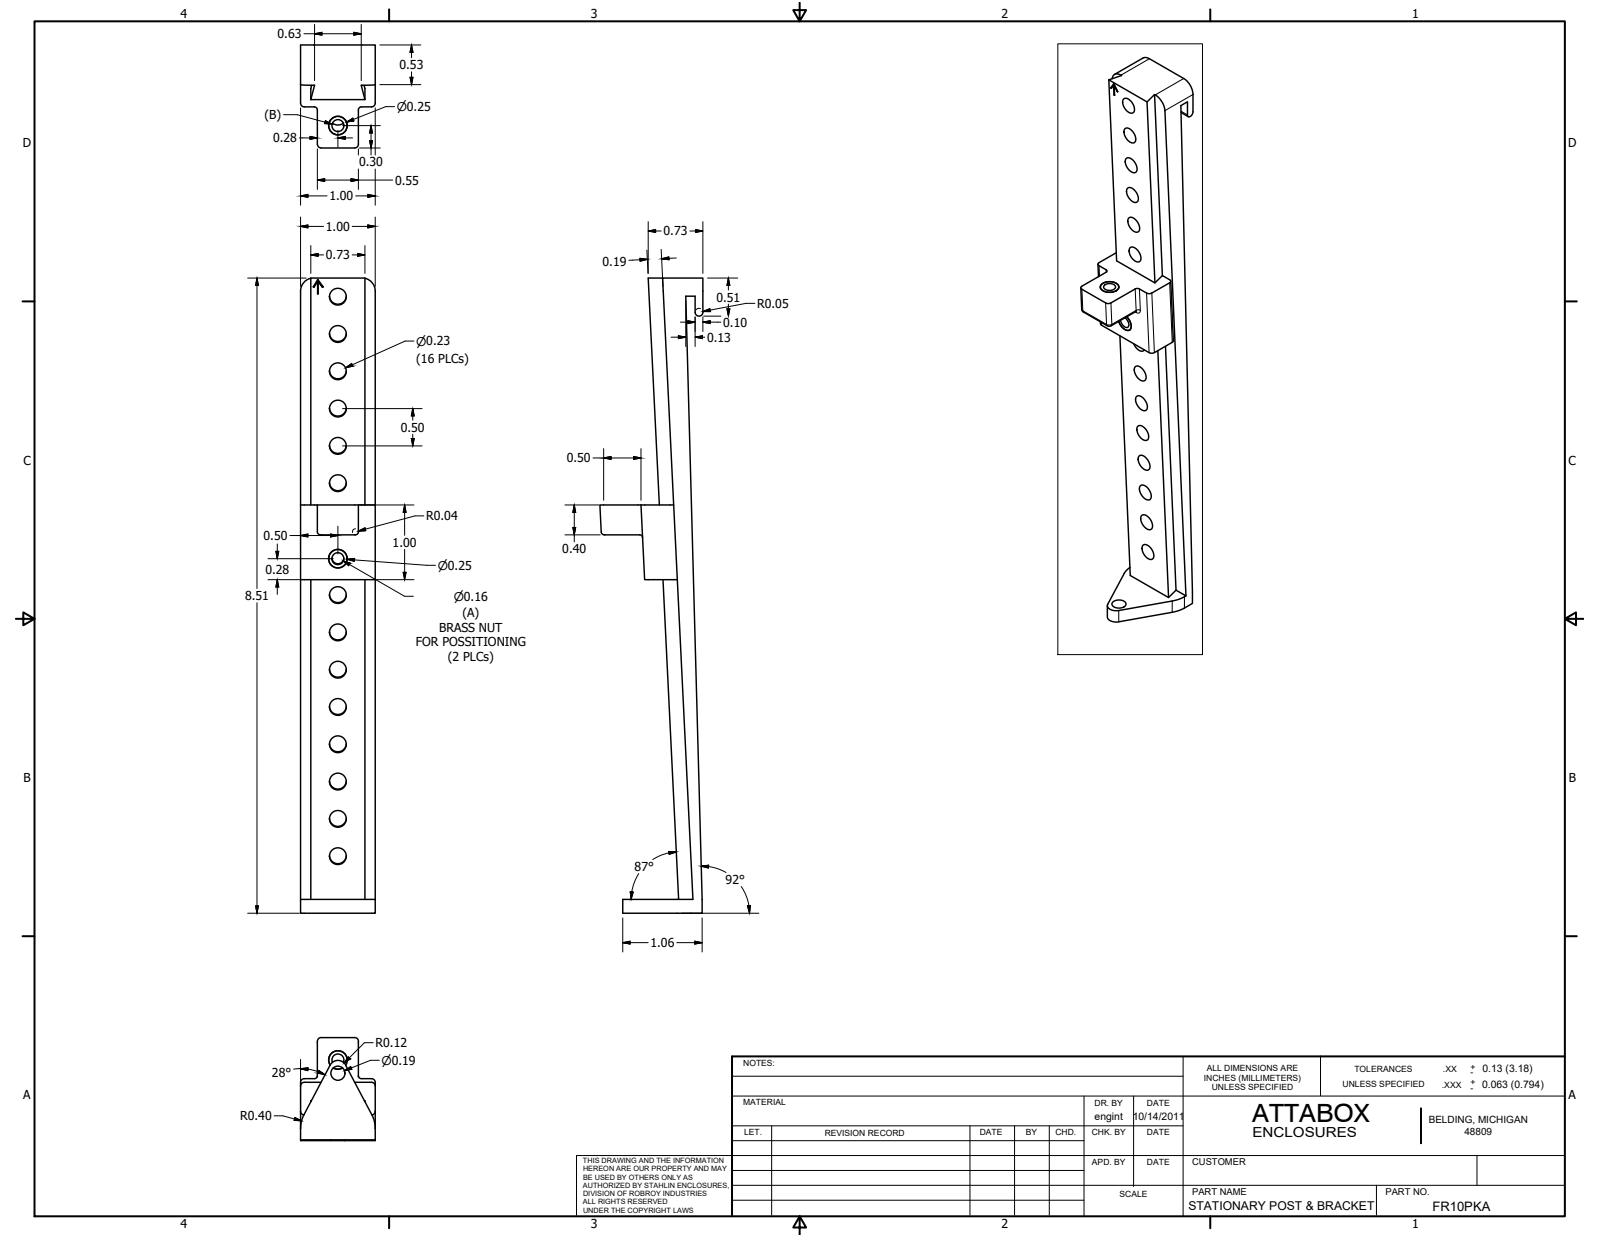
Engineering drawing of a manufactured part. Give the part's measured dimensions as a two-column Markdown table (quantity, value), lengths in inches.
| quantity | value |
| --- | --- |
| part name | FR10PKA |
| STEP written by | SolidWorks 2019 (AUTOMOTIVE_DESIGN) |
| units | inches |
| bodies | 25 solids, 2320 faces (1270 planar, 350 cylindrical, 700 other) |
| overall size | 20.754 × 16.753 × 8.703 |
| volume | 13.69 in³ |
| surface area | 161.8 in² |
| round holes (diameter × count) | 0.25 × 64, 0.253 × 8, 0.217 × 4, 0.22 × 4, 0.156 × 1 |
| round bosses / shafts (diameter × count) | 0.19 × 12, 0.373 × 8, 0.433 × 4, 0.315 × 4, 0.246 × 1 |
| partial cylindrical surfaces (radius × count) | 0.01 × 168, 0.06 × 52, 0.049 × 4, 0.23 × 4 |
| main face-to-face distances | 24.021, 2.828, 1, 10.096, 13.925, 11.096, 12.925, 0.203, 10.299, 11.299 |
| hole center spacings | 0.5, 1, 2.873, 3, 1.5, 3.202, 2, 3.465 |
